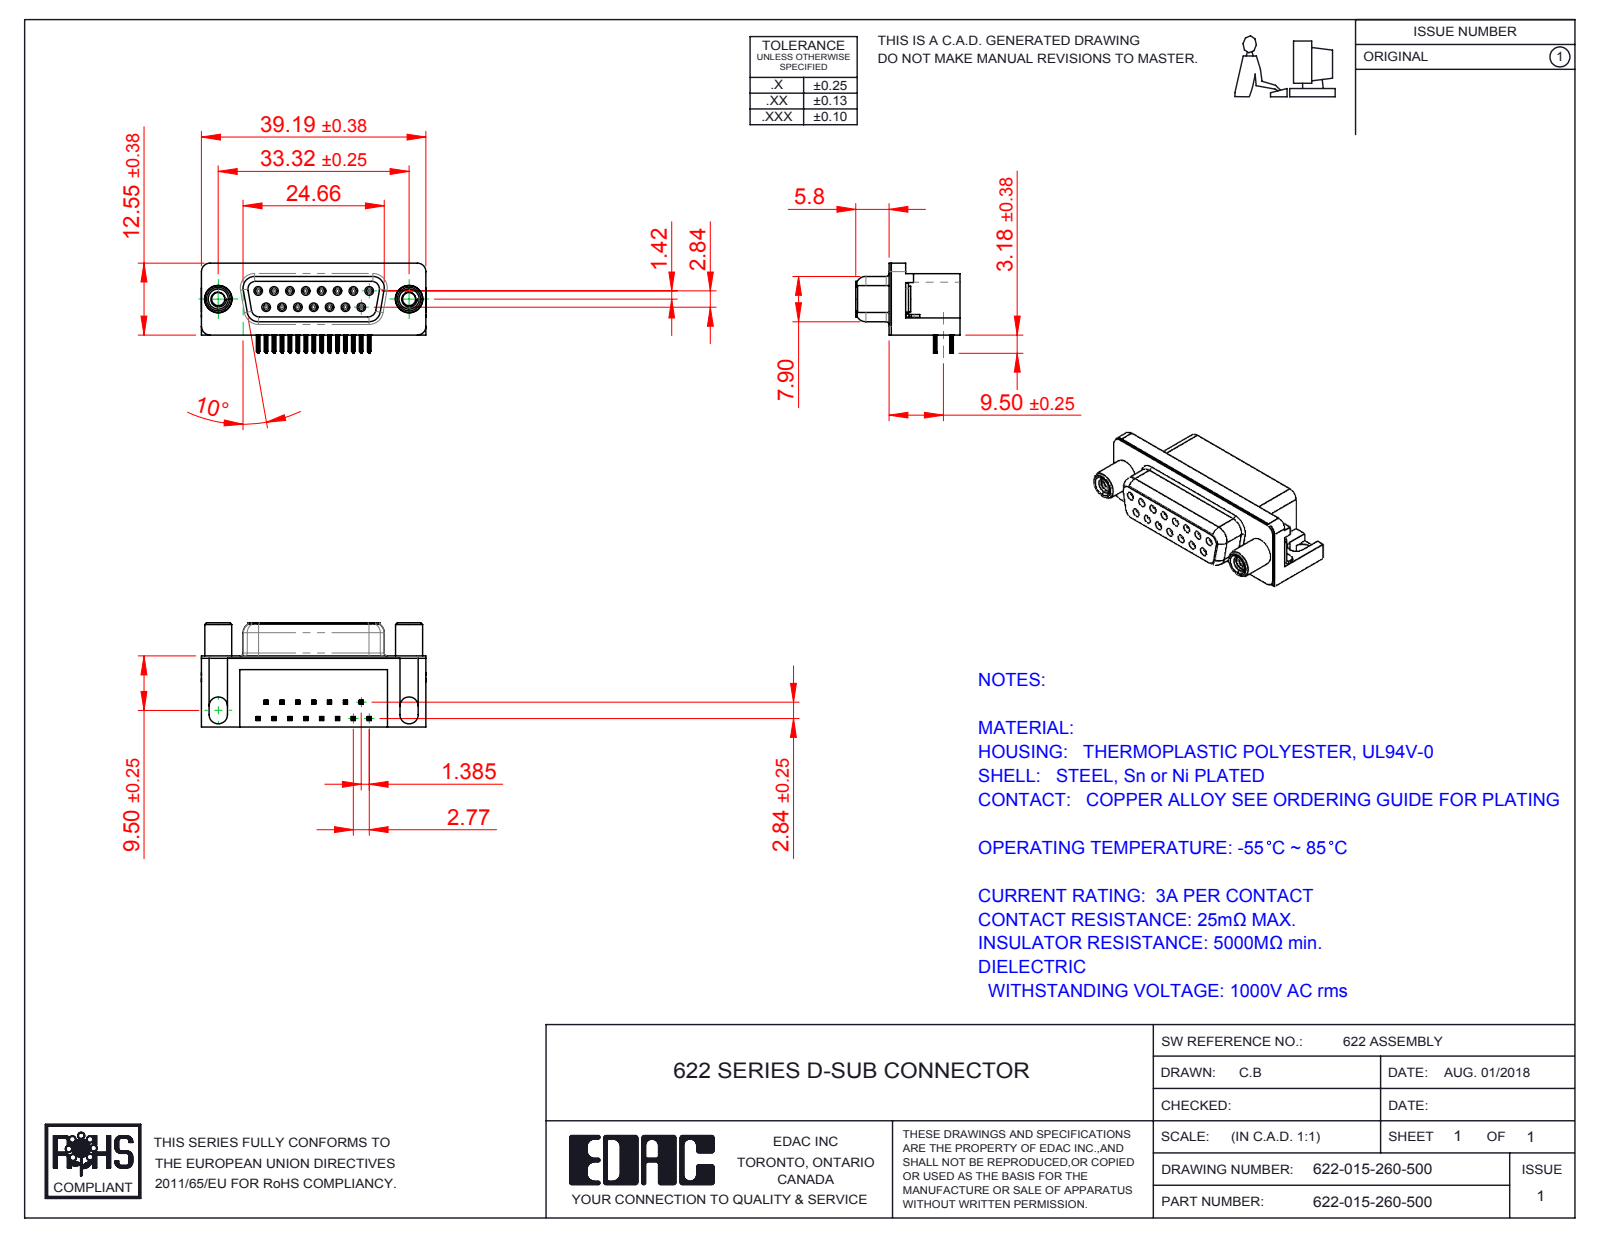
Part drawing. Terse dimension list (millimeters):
name: 622 Round Threaded Standoff; 622 Contact Top; 622 Housing_15 Socket; 622-015-260-500 (+3 more)
written by: SolidWorks 2016 (CONFIG_CONTROL_DESIGN)
unit: mm
bodies: 21 solids, 2417 faces (1066 planar, 609 cylindrical, 742 other)
size: 39.22 × 18.2 × 15.73
volume: 5 242 mm³; area: 6 742 mm²
holes: 15× ⌀0.8, 15× ⌀0.9, 2× ⌀2.3, 2× ⌀3.1, 2× ⌀4, 2× ⌀4.8, 2× ⌀5
bosses: 15× ⌀1.2, 2× ⌀4.9, 2× ⌀4.7, 2× ⌀4.5, 2× ⌀3.85
rounds: 120× R0.1, 60× R0.15, 30× R0.35, 18× R1, 15× R0.34, 8× R1.35, 8× R1.5, 8× R1.6
face distances: 0.4, 12, 6.2, 10.35, 12.4, 2.9, 0.45, 2.84, 9.5, 2.5
hole spacings: 3.16, 2.77, 5.54, 8.31, 11.08, 5.03, 5.04, 7.48
